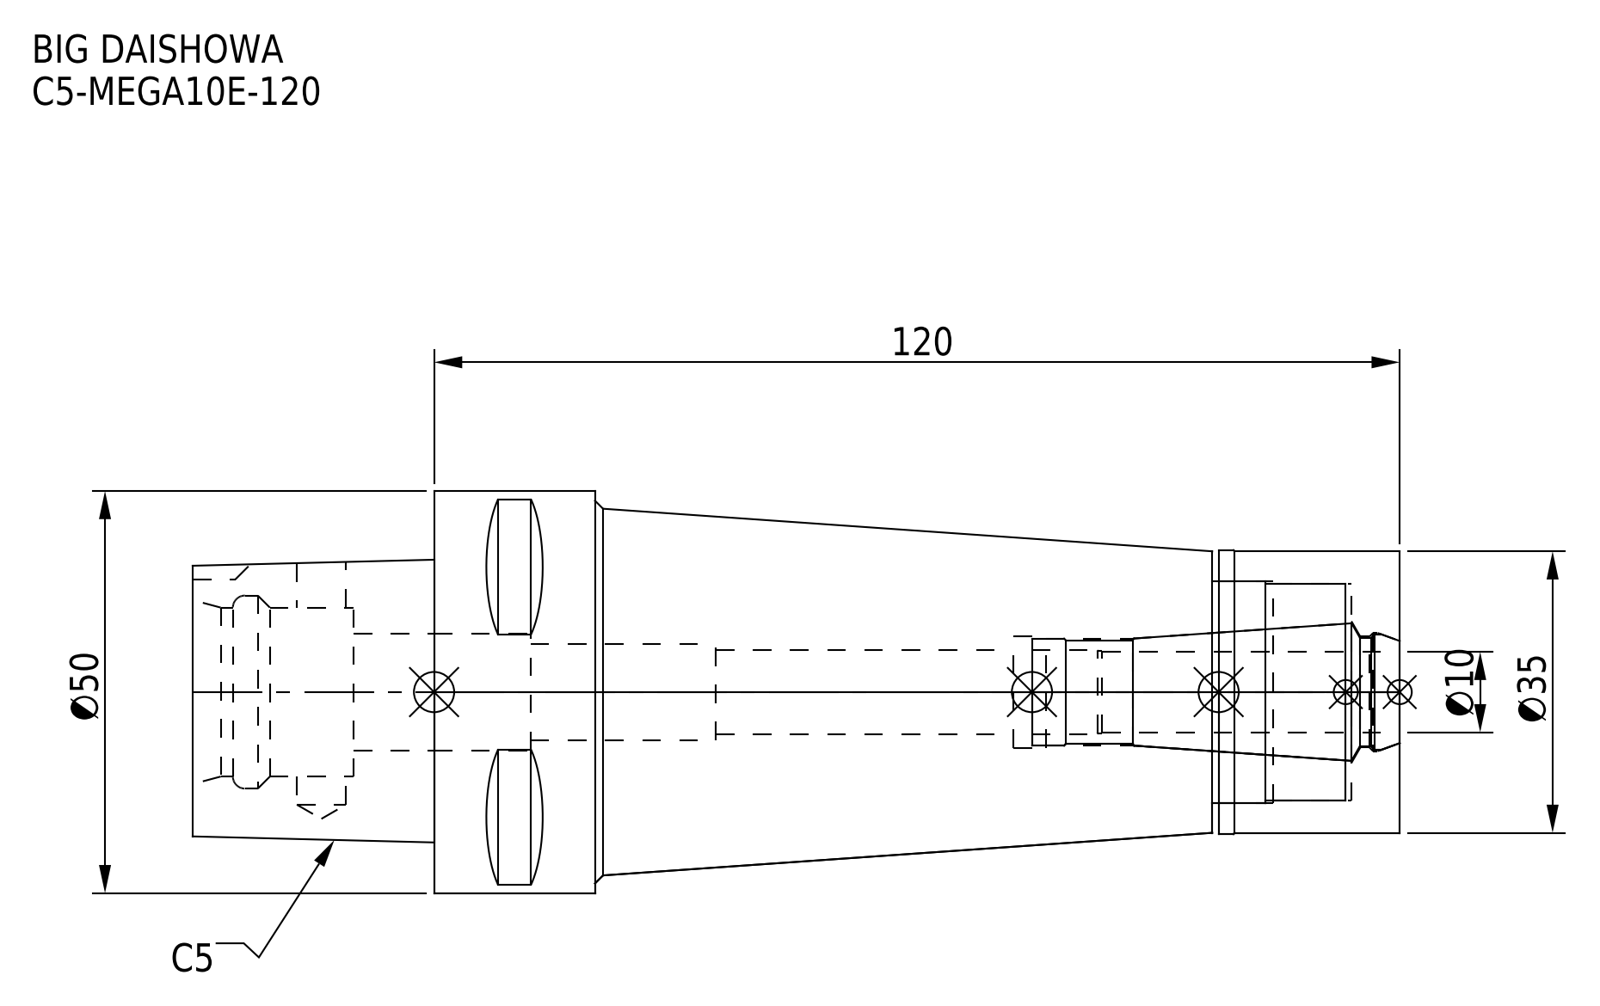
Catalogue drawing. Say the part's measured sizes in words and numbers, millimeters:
The part is named "C5-MEGA10E-120; C5-MEGA10E-120-100_ASM.stp; DXF_TEMP_ASSY_ASM_4_ASM.stp; MEN10_1.stp (+3 more)". Its 3-D file was written by "SolidWorks 2019 (CONFIG_CONTROL_DESIGN)". It is 2 solids with 100 faces: 37 planar, 39 cylindrical and 24 other. Overall it measures 150 by 50 by 50 millimeters. Its volume is 161 406 cubic millimeters and its surface area 32 922 square millimeters. Round holes: 1 of diameter 6.1, 1 of diameter 10.4, 1 of diameter 12, 1 of diameter 13.3, 1 of diameter 13.8, 1 of diameter 13.9, 1 of diameter 14.5, 1 of diameter 14.7, 1 of diameter 21, 1 of diameter 24, 1 of diameter 27, 1 of diameter 27.5. Round bosses or shafts: 1 of diameter 50, 1 of diameter 35.3, 1 of diameter 35. Partial cylindrical surfaces (rounded edges, fillets, slot ends): 1 of radius 4. The main face-to-face distances are 120, 30, 22.5, 97.5, 150, 127.5, 96.7, 23.3, 0.8, 126.7.
